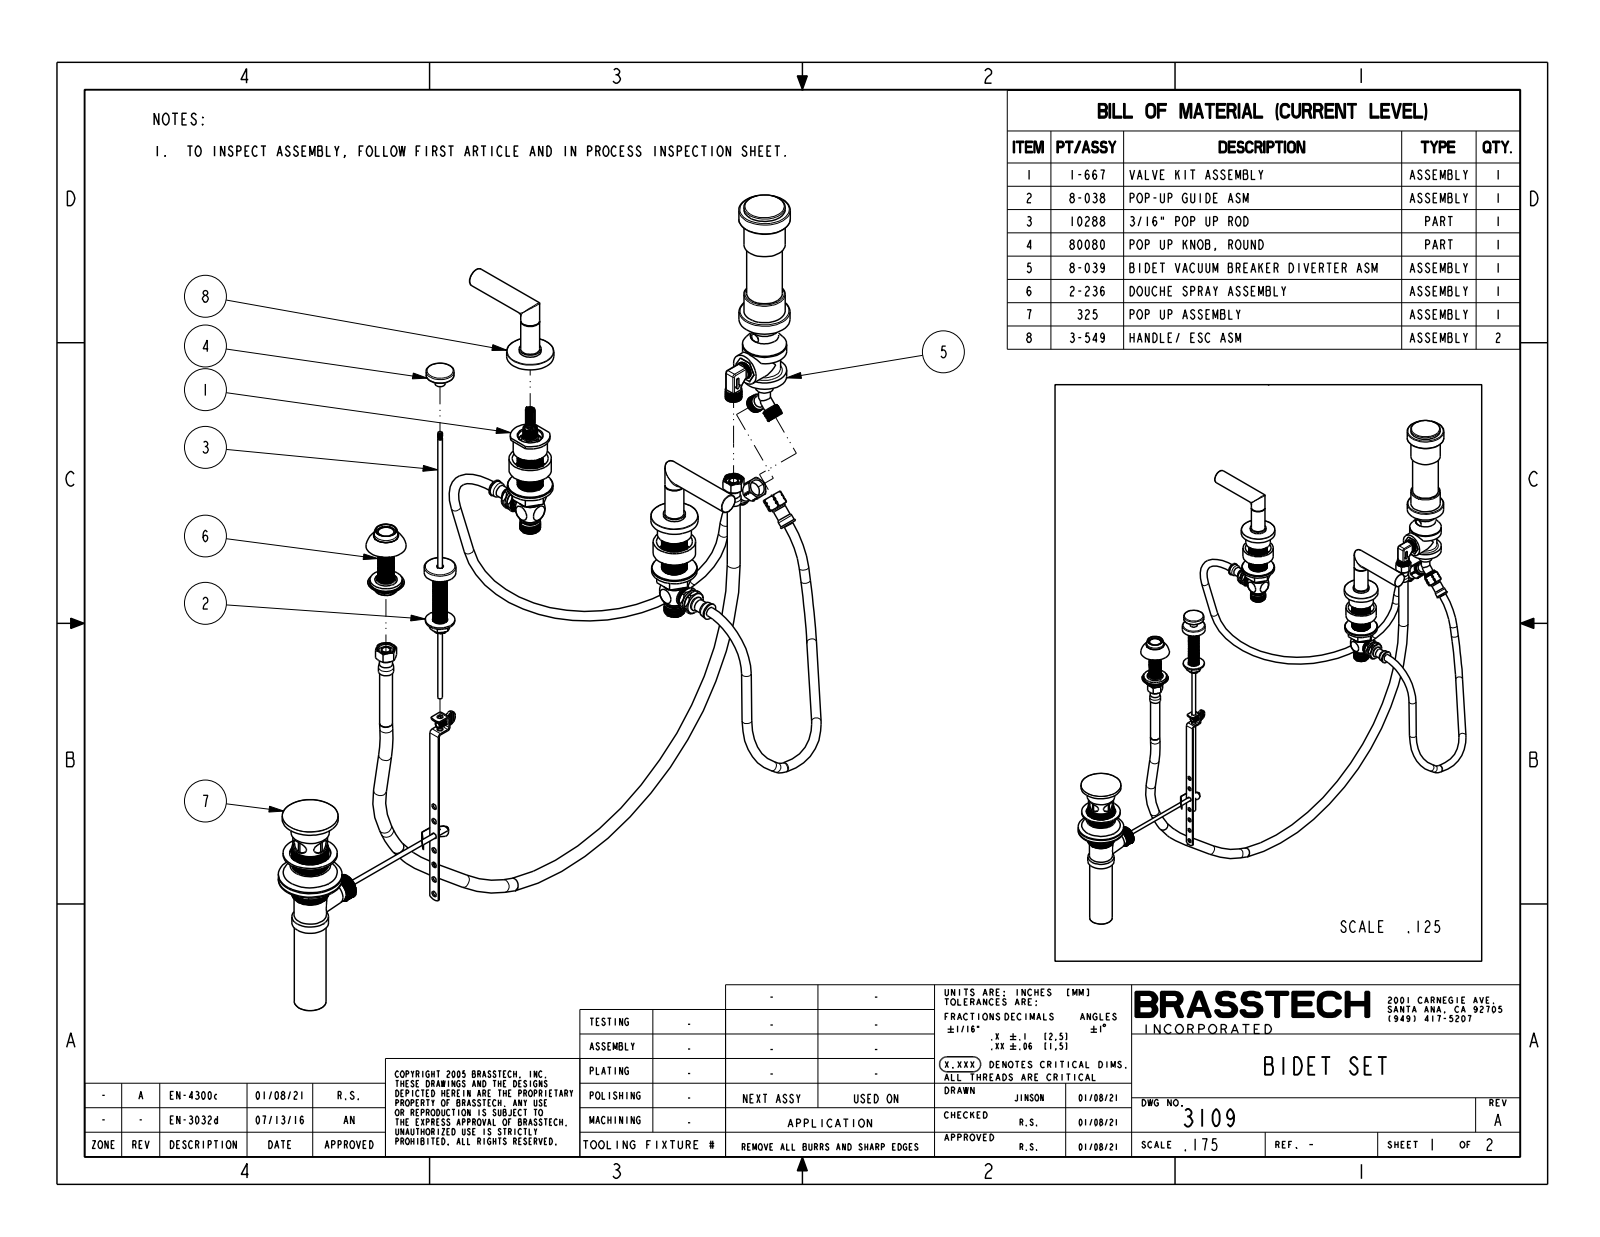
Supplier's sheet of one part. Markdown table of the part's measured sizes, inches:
| quantity | value |
| --- | --- |
| part name | 3109 |
| STEP written by | CREO PARAMETRIC BY PTC INC, 2018400 (CONFIG_CONTROL_DESIGN) |
| units | inches |
| bodies | 5 solids, 176 faces (58 planar, 68 cylindrical, 50 other) |
| overall size | 22.8 × 14 × 5.445 |
| volume | 18.33 in³ |
| surface area | 90.22 in² |
| round holes (diameter × count) | 0.76 × 2, 0.625 × 1, 0.792 × 1, 0.94 × 1 |
| round bosses / shafts (diameter × count) | 0.75 × 3, 1.85 × 2, 0.86 × 2, 0.506 × 2, 2.02 × 1, 2 × 1, 1.62 × 1, 1.4 × 1 |
| partial cylindrical surfaces (radius × count) | 0.357 × 1 |
| main face-to-face distances | 0.25, 5.445, 5.195, 0.31, 0.94, 0.5, 4.545, 0.06, 5.135, 5.295 |
| hole center spacings | 12.649, 8 |
